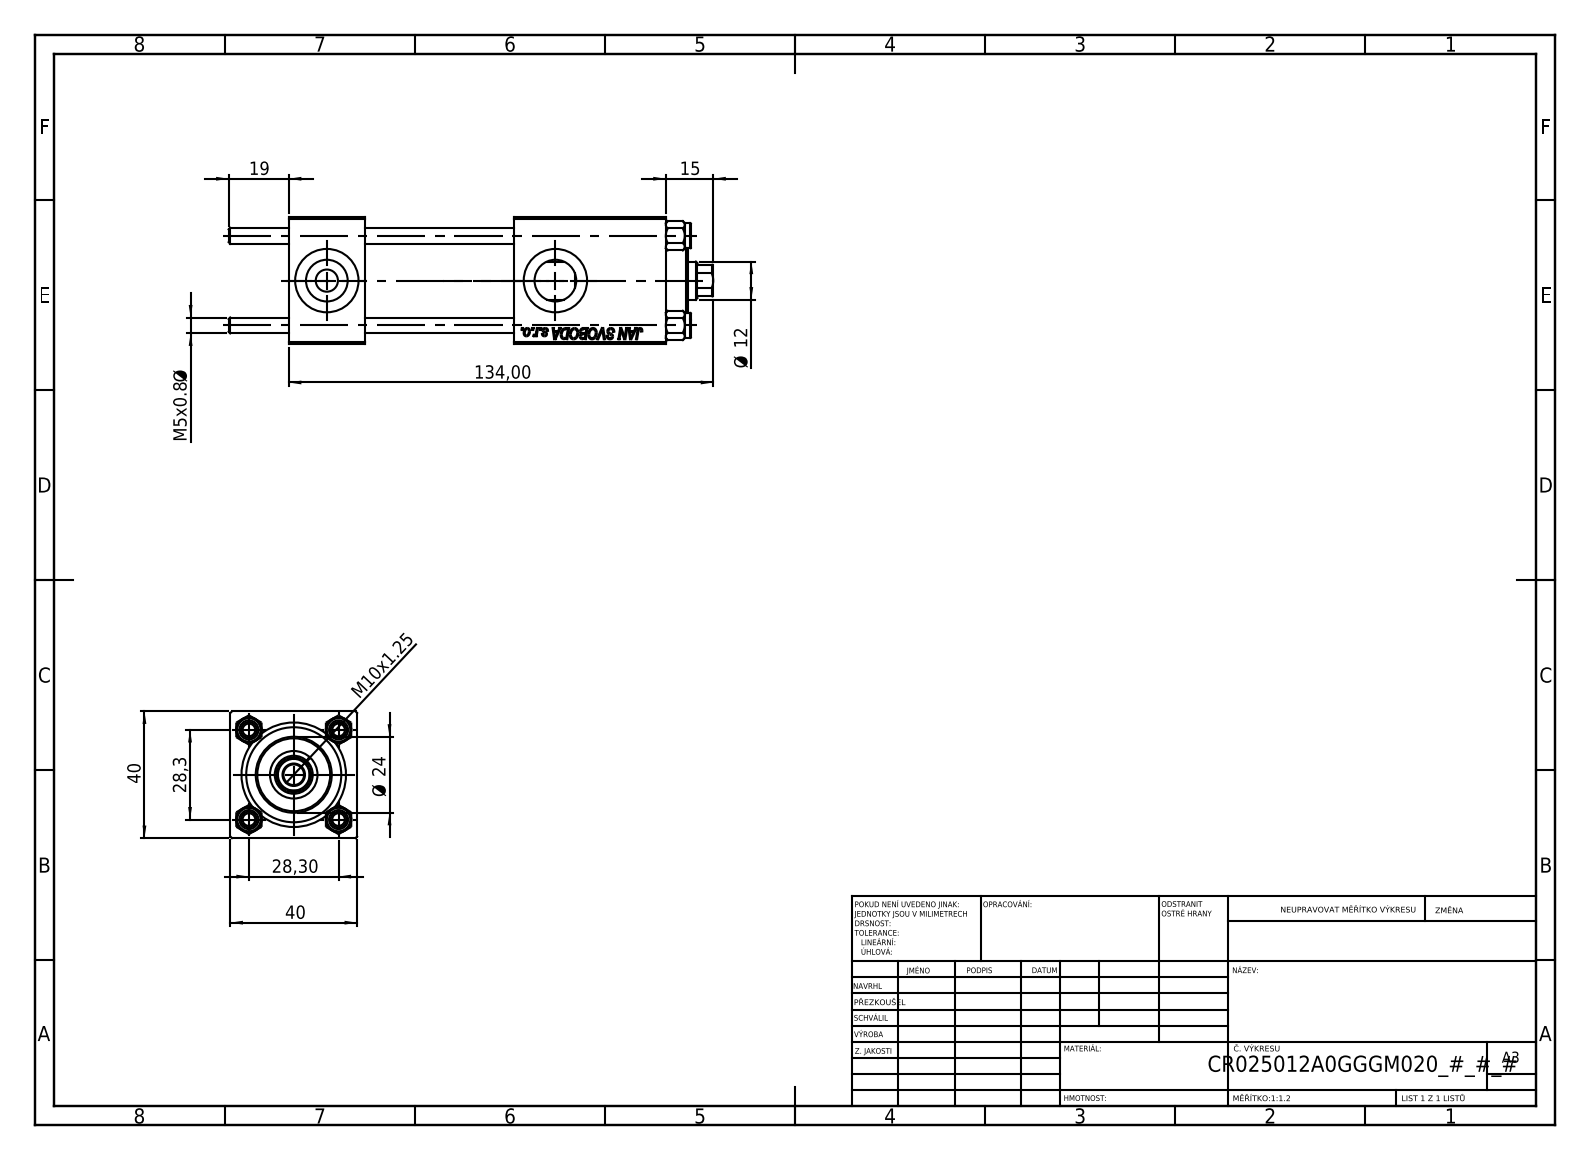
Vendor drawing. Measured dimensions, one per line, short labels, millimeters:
name: V215_VC_A; V215CR_BODY_A; CR025_012_A_0_G_A_G_M_020_+#_##_TYCINKA; NUT_M5 (+1 more)
written by: SolidWorks 2019 (CONFIG_CONTROL_DESIGN)
unit: mm
bodies: 11 solids, 1132 faces (517 planar, 79 cylindrical, 536 other)
size: 153 × 40 × 40
volume: 144 747 mm³; area: 58 863 mm²
holes: 4× ⌀5, 3× ⌀20, 2× ⌀7, 2× ⌀13.16, 1× ⌀6.5, 1× ⌀12, 1× ⌀15, 1× ⌀25, 1× ⌀30
bosses: 4× ⌀8, 1× ⌀31, 1× ⌀24
rounds: 1× R5.5
face distances: 40, 24, 119, 95, 90.3, 66.3, 28.7, 71, 47, 19.3
hole spacings: 20.01, 28.3, 40.02, 72.16
